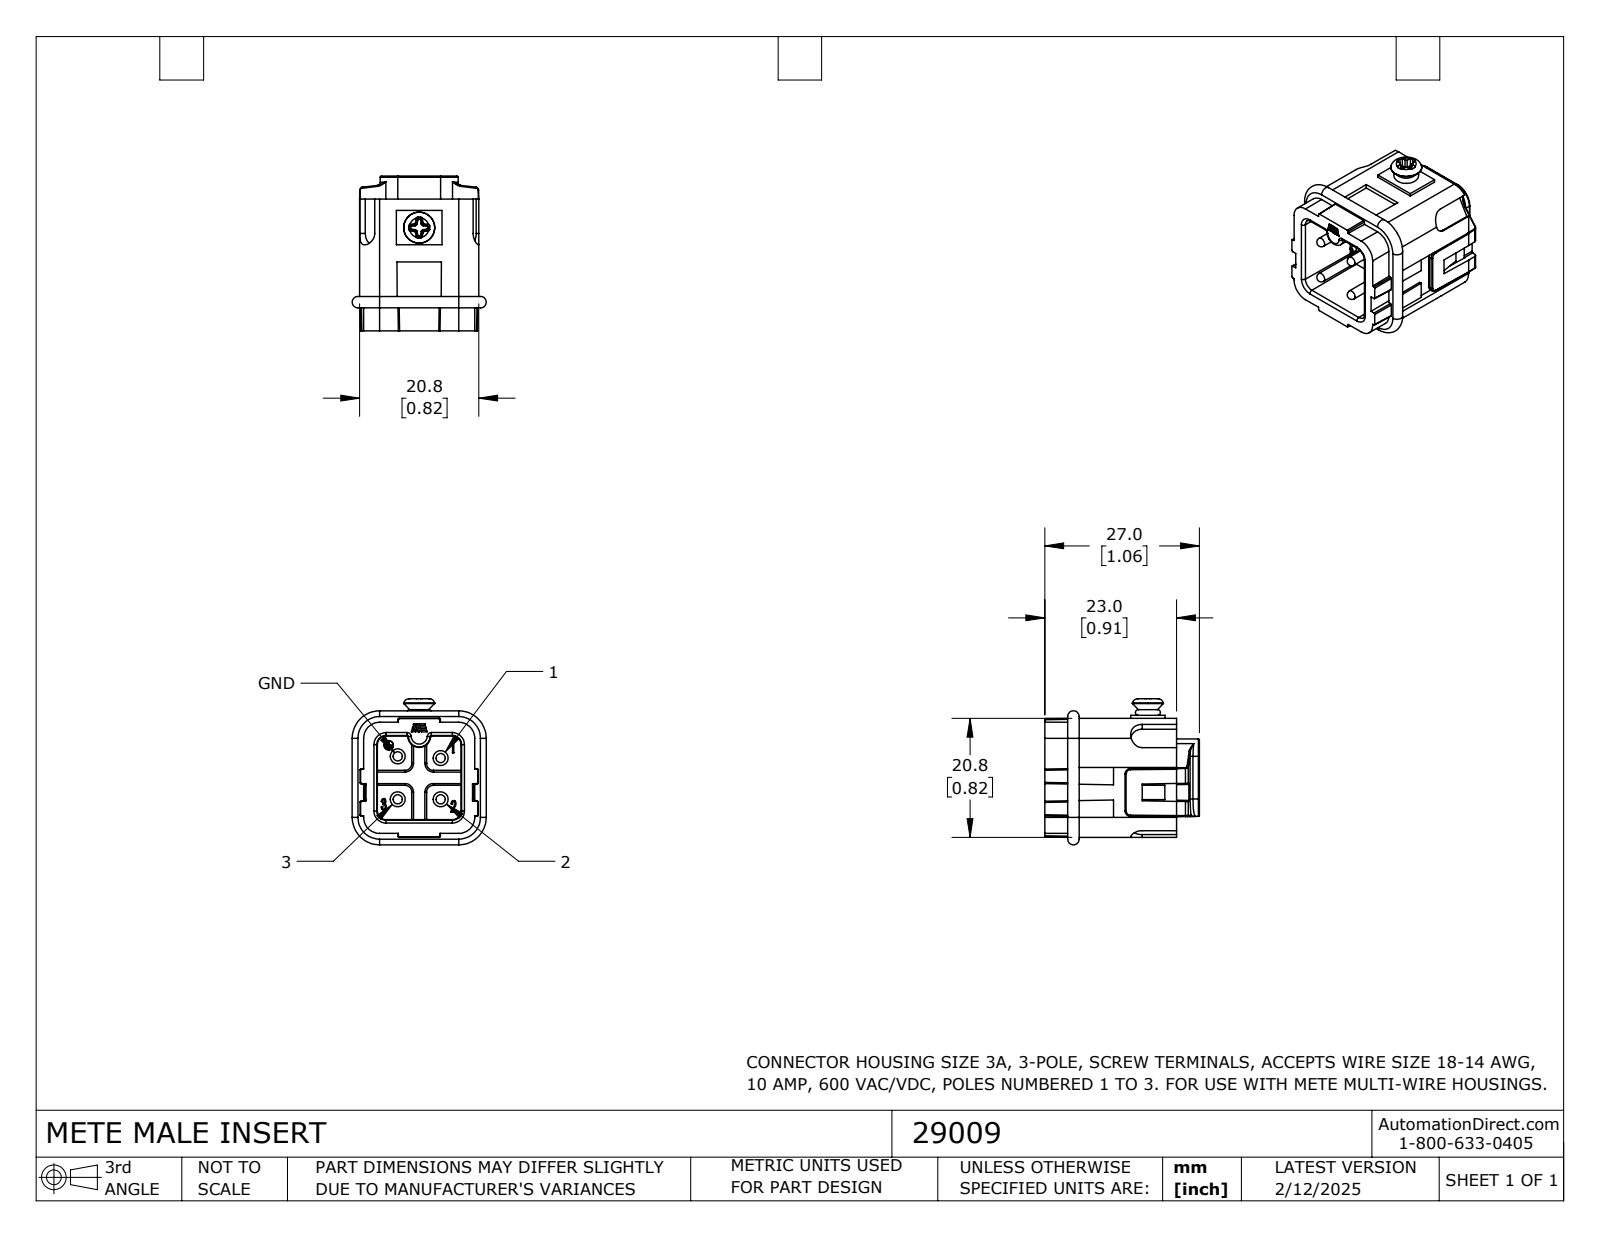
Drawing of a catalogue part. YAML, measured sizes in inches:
part_name: "29009"
step_written_by: "SolidWorks 2024 (CONFIG_CONTROL_DESIGN)"
units: inches
bodies: {solids: 1, faces: 556, planar: 268, cylindrical: 149, other: 139}
overall_size: [1.063, 1.004, 0.921]
volume: 0.474
surface_area: 7.649
round_holes:
  - {diameter: 0.102, count: 4}
  - {diameter: 0.061, count: 1}
round_bosses_or_shafts:
  - {diameter: 0.113, count: 4}
  - {diameter: 0.093, count: 4}
  - {diameter: 0.063, count: 4}
  - {diameter: 0.065, count: 1}
partial_cylinders:
  - {radius: 0.008, count: 40}
  - {radius: 0.012, count: 16}
  - {radius: 0.004, count: 12}
  - {radius: 0.02, count: 8}
  - {radius: 0.039, count: 6}
  - {radius: 0.079, count: 5}
  - {radius: 0.059, count: 4}
  - {radius: 0.11, count: 4}
face_to_face_distances: [0.028, 0.791, 0.453, 0.819, 0.748, 0.906, 0.157, 0.043, 0.776, 0.039]
hole_center_spacings: [0.295, 0.098, 0.283, 0.296, 0.368, 0.376, 0.409, 0.418]
